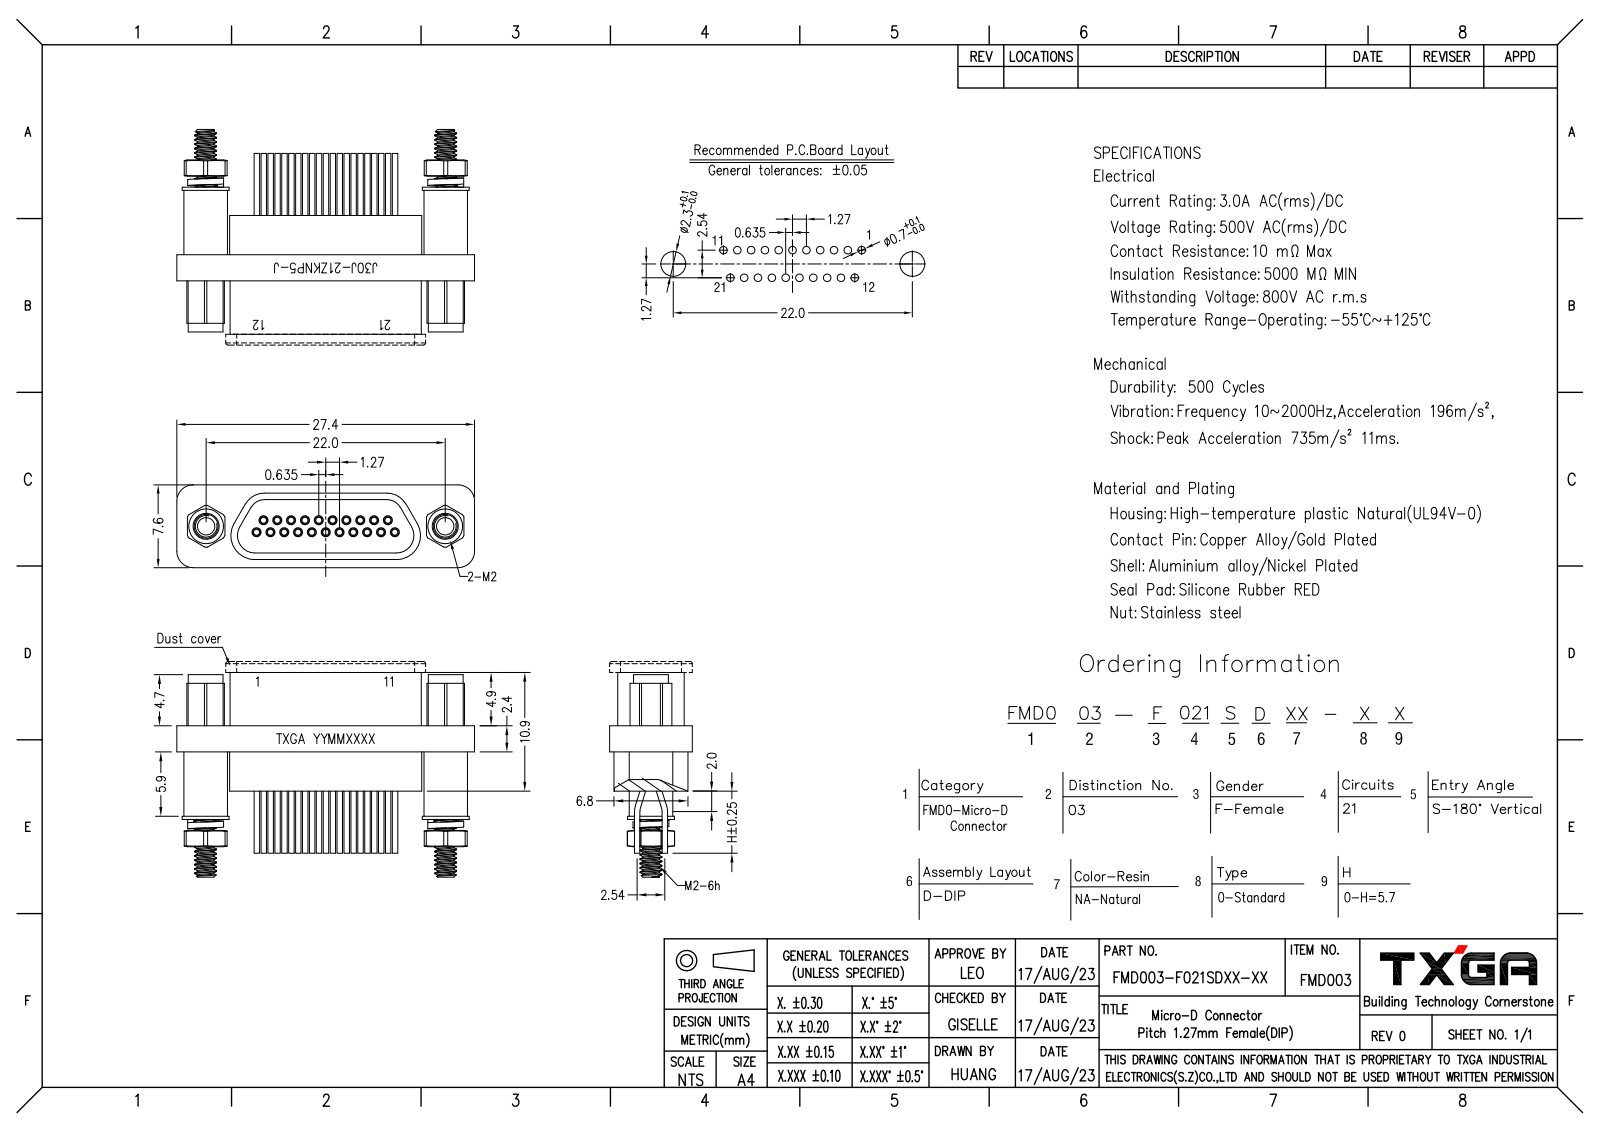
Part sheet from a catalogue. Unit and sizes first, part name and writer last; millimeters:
Units: millimetres
Overall size (bounding box): 27.4 × 18.8 × 7.6
Round holes (diameter × count): ⌀0.6 ×21, ⌀1.6 ×2, ⌀2.1 ×2, ⌀2.2 ×2, ⌀2.3 ×2, ⌀3.2 ×2
Round bosses / shafts (diameter × count): ⌀0.5 ×63, ⌀0.8 ×21, ⌀4.3 ×2, ⌀4 ×2, ⌀3.5 ×2, ⌀3.1 ×2, ⌀2 ×2
Partial cylindrical surfaces — rounded edges, fillets, slot ends (radius × count): R0.3 ×12, R1.5 ×4, R1.6 ×4, R1.8 ×4, R2.2 ×4
Main face-to-face distances: 0.6, 6, 0.75, 6.25, 1.35, 6.85, 7.2, 5.5, 0.95, 0.4
Hole centre spacings: 1.27, 2.2, 2.54, 3.36, 3.81, 5.08, 6.35, 7.62
Volume: 1 322 mm³ · Surface area: 2 514 mm²
Bodies: 1 solid, 1637 faces (657 planar, 478 cylindrical, 502 other)
Part name (STEP PRODUCT): FMD003-F021SDNA-00
STEP written by: SolidWorks 2021 (CONFIG_CONTROL_DESIGN)
